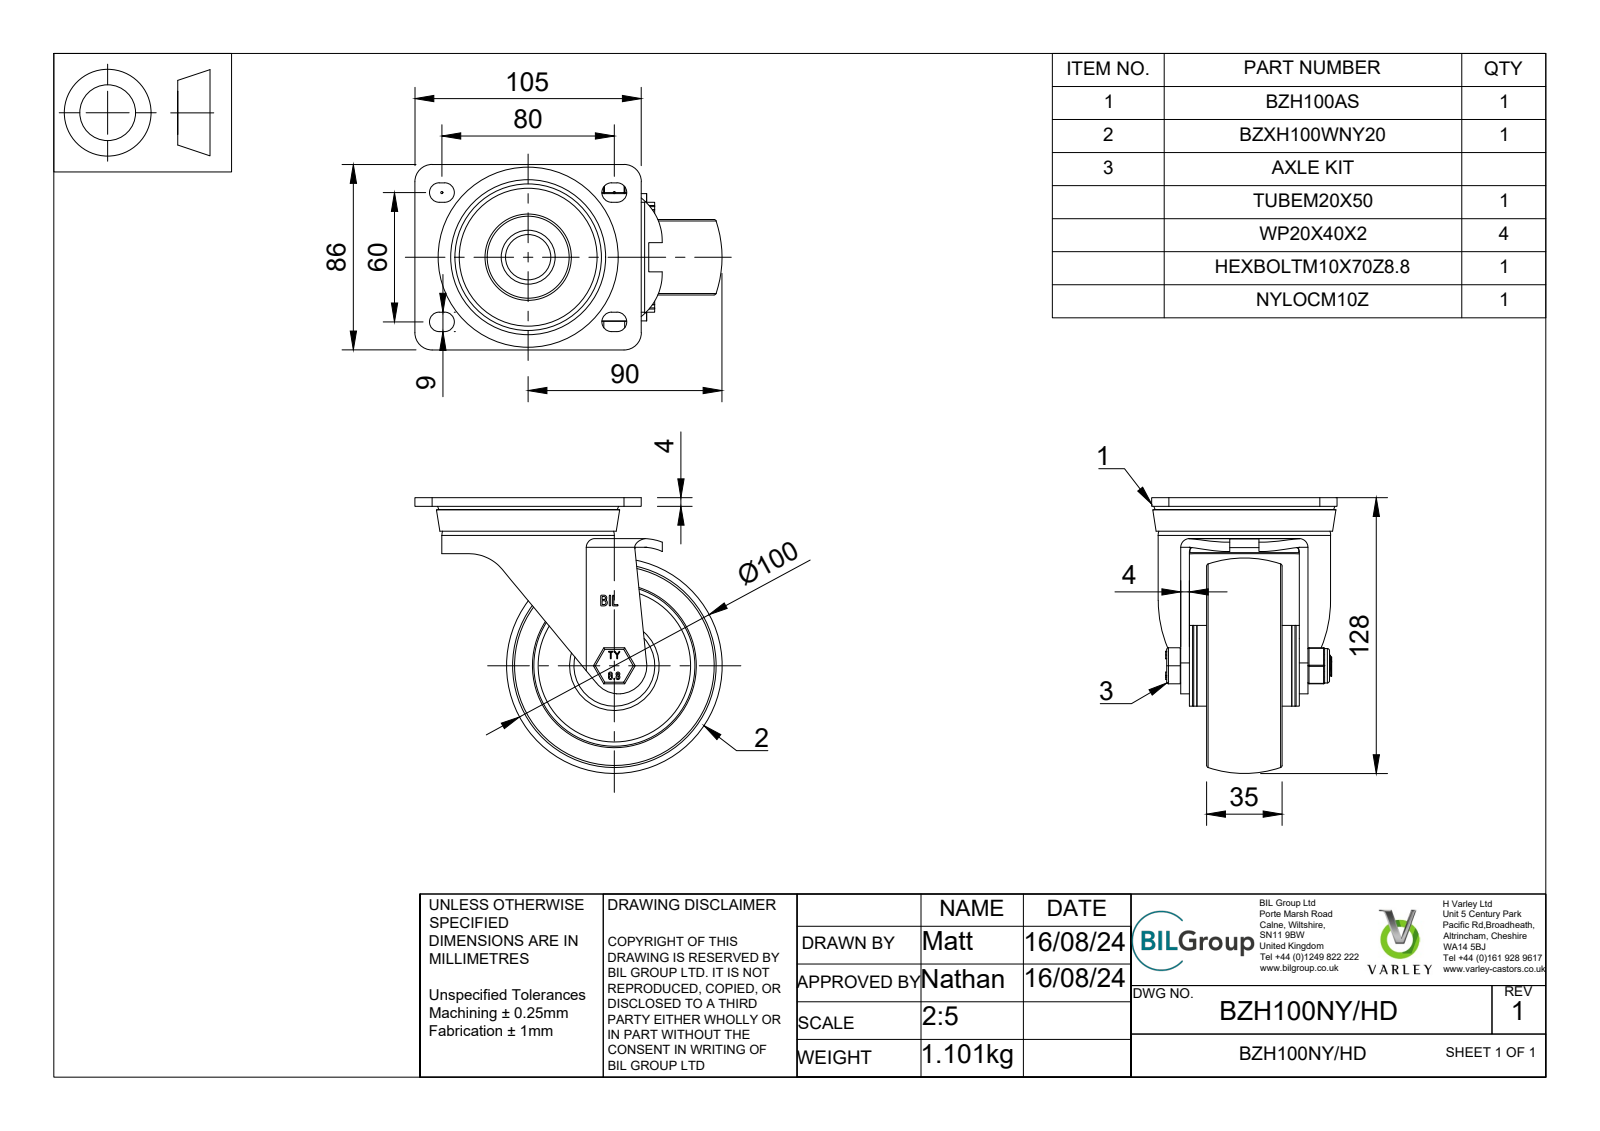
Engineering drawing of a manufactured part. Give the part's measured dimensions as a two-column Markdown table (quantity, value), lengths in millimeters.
| quantity | value |
| --- | --- |
| part name | BZH100NY/HD v4; BZH100AS - 2 v1; ZINC PLATED, PRESSED STEEL TOP PLATE (1); ZINC PLATED, PRESSED STEEL FORKS (1) (+7 more) |
| STEP written by | Autodesk Translation Framework v13.14.0.145 (AUTOMOTIVE_DESIGN) |
| units | millimeters |
| bodies | 12 solids, 396 faces (177 planar, 125 cylindrical, 94 other) |
| overall size | 142.5 × 128 × 86 |
| volume | 326 398 mm³ |
| surface area | 115 951 mm² |
| round holes (diameter × count) | 10 × 1, 10.2 × 1, 10.5 × 1, 12 × 1, 20.1 × 1, 21 × 1, 25 × 1, 32 × 1, 72 × 1 |
| round bosses / shafts (diameter × count) | 80 × 1, 50.5 × 1, 37.5 × 1, 31 × 1, 20 × 1, 19.9 × 1, 16 × 1, 9.85 × 1 |
| partial cylindrical surfaces (radius × count) | 0.5 × 18, 4.5 × 8, 0.75 × 6, 2 × 4, 8 × 4, 4 × 2, 25.41 × 2, 13.03 × 1 |
| main face-to-face distances | 4, 7.5, 21, 22, 1.5, 47.5, 13, 3.5, 30, 47 |
